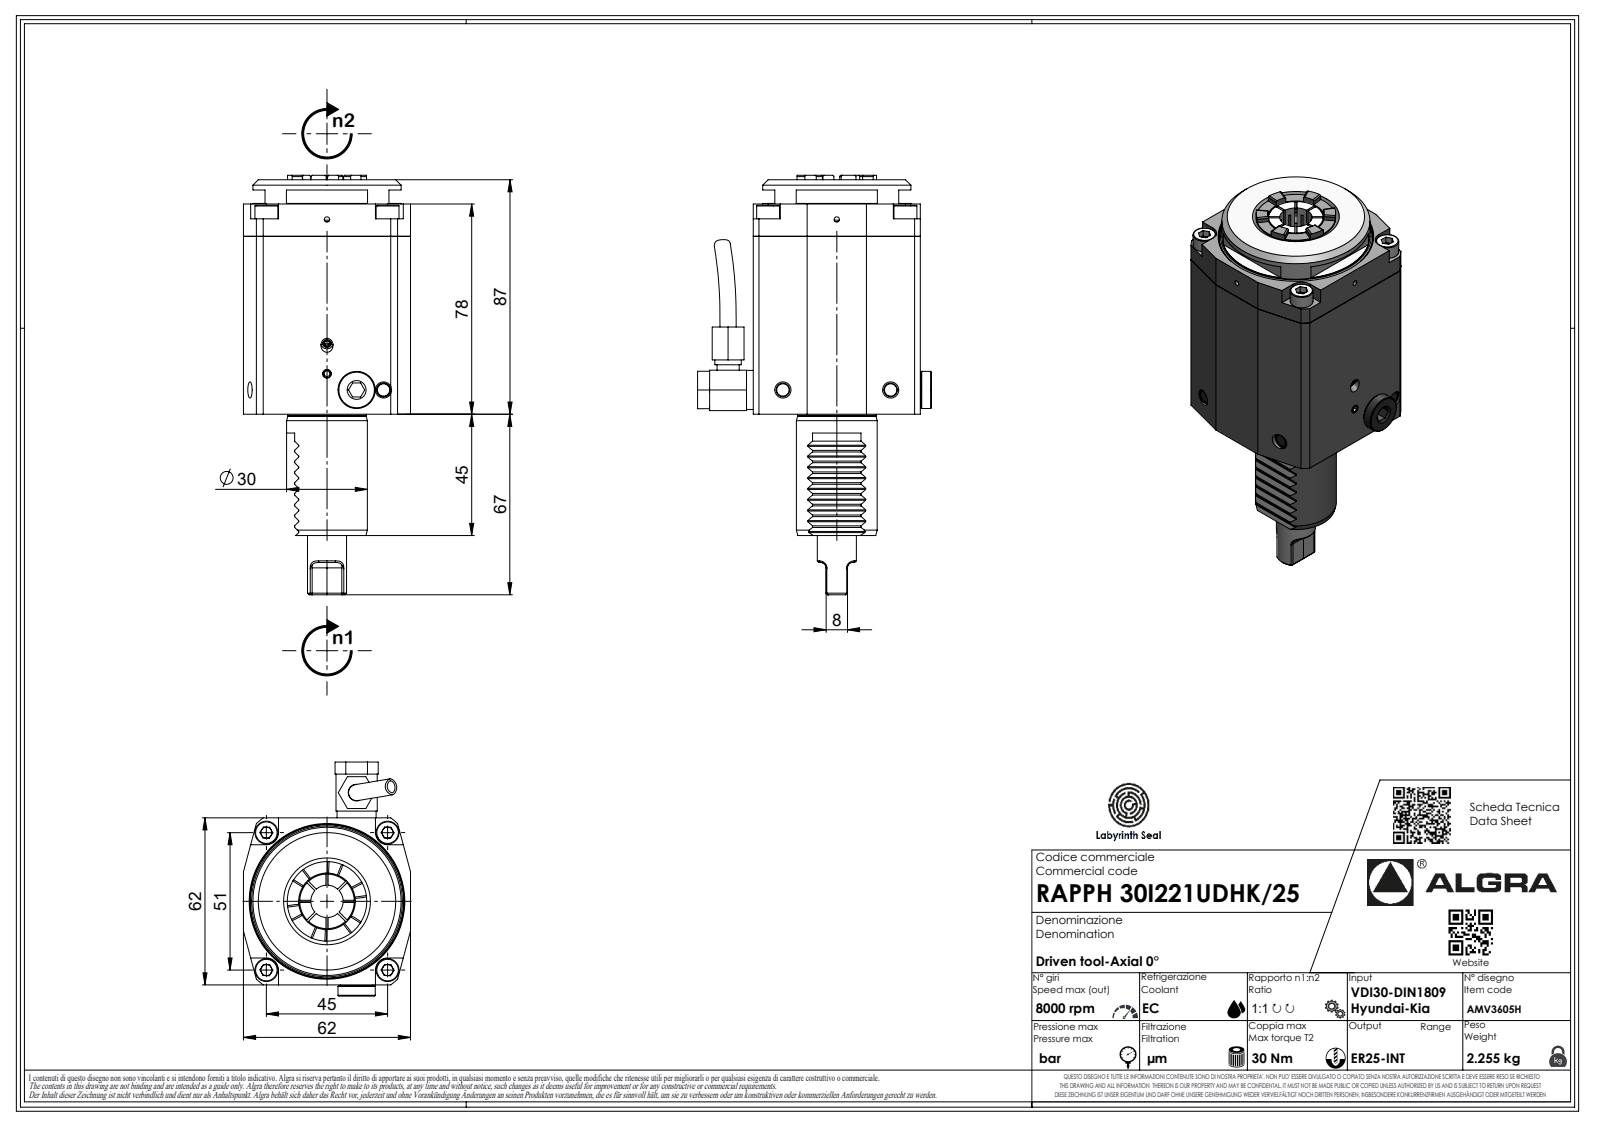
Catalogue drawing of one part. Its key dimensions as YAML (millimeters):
part_name: "RAPPH30I221UDHK25"
step_written_by: "SolidWorks 2023 (AUTOMOTIVE_DESIGN)"
units: millimeters
bodies: {solids: 1, faces: 538, planar: 343, cylindrical: 80, other: 115}
overall_size: [155.65, 86.85, 62]
volume: 341902
surface_area: 35265
round_holes:
  - {diameter: 2.1, count: 1}
round_bosses_or_shafts:
  - {diameter: 14.5, count: 2}
  - {diameter: 55, count: 1}
  - {diameter: 30, count: 1}
  - {diameter: 29.1, count: 1}
  - {diameter: 13.8, count: 1}
  - {diameter: 12, count: 1}
  - {diameter: 9.8, count: 1}
  - {diameter: 8.2, count: 1}
partial_cylinders:
  - {radius: 35, count: 10}
  - {radius: 0.3, count: 9}
  - {radius: 0.33, count: 7}
  - {radius: 0.52, count: 7}
  - {radius: 3.7, count: 7}
  - {radius: 2, count: 6}
  - {radius: 0.21, count: 1}
  - {radius: 7.65, count: 1}
face_to_face_distances: [62, 65.58, 87, 78, 9, 8, 54, 2.83, 45, 123]
